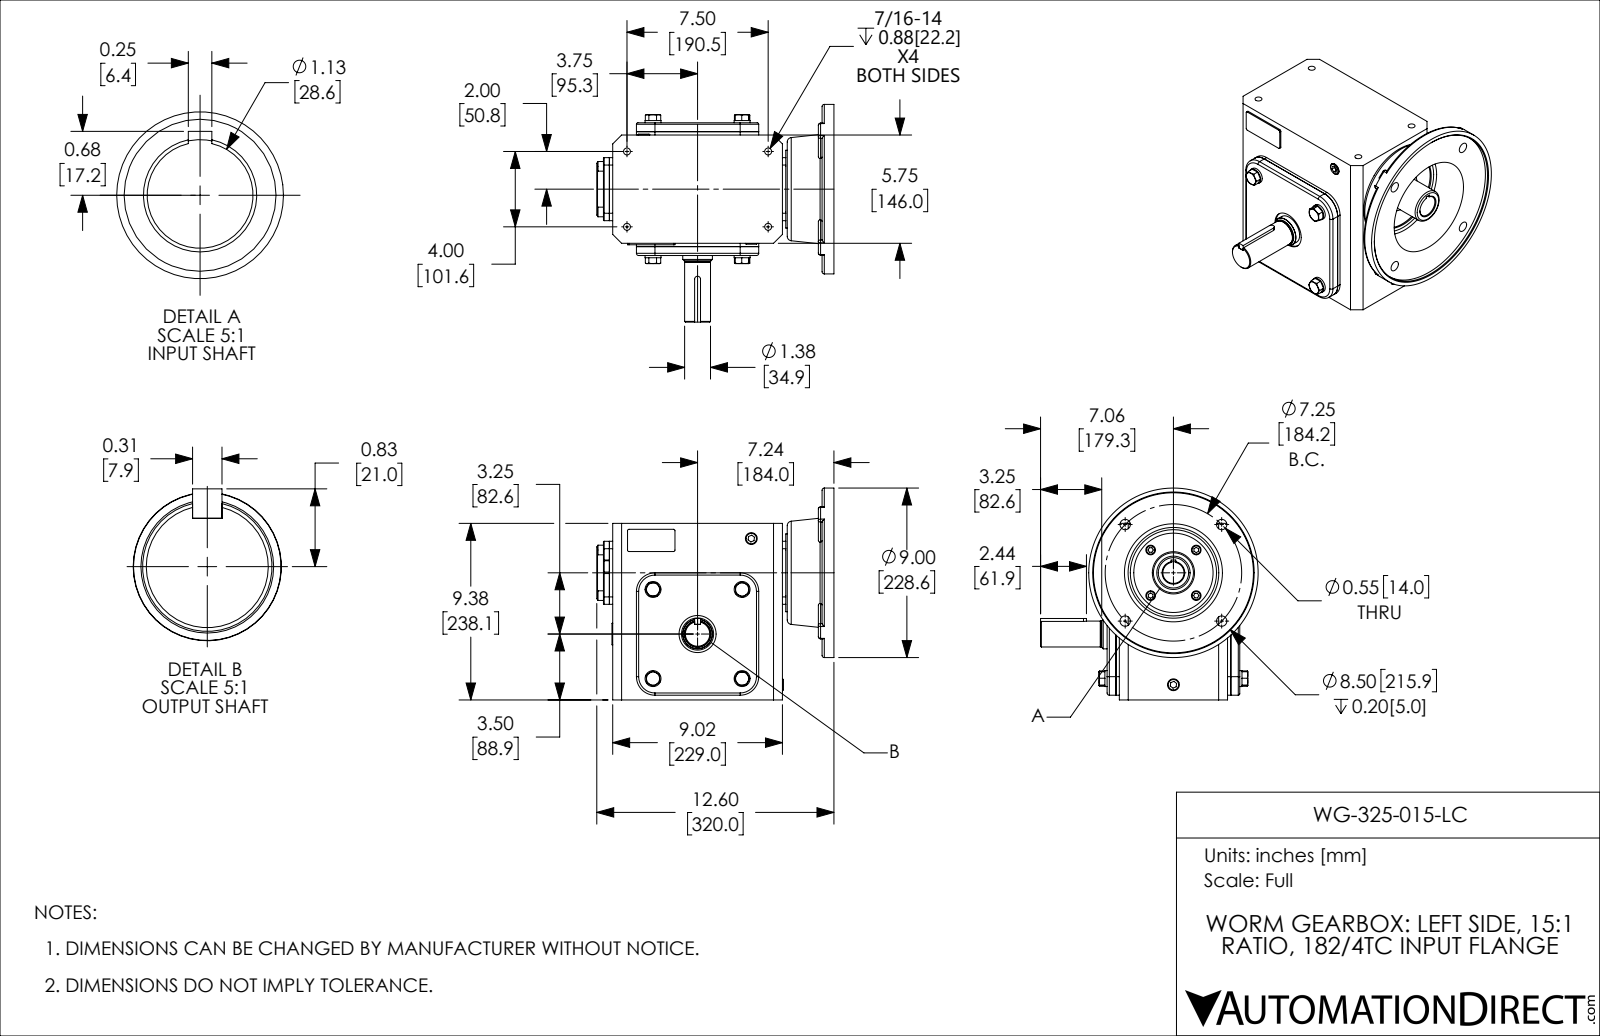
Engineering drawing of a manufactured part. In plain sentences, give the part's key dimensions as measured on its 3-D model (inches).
The part is named "WG-325-015-LC". Its 3-D file was written by "SolidWorks 2017 (AUTOMOTIVE_DESIGN)". It is 40 solids with 653 faces: 336 planar, 195 cylindrical and 122 other. Overall it measures 12.598 by 11.559 by 11.25 inches. Its volume is 529.7 cubic inches and its surface area 1 026 square inches. Round holes: 4 of diameter 0.354, 4 of diameter 0.368, 4 of diameter 0.551, 3 of diameter 0.628, 1 of diameter 0.591, 1 of diameter 0.978, 1 of diameter 1.125, 1 of diameter 1.181, 1 of diameter 1.969, 1 of diameter 2.244, 1 of diameter 2.441, 1 of diameter 2.756. Round bosses or shafts: 4 of diameter 0.846, 4 of diameter 0.512, 1 of diameter 9, 1 of diameter 4.134, 1 of diameter 2.835, 1 of diameter 1.772, 1 of diameter 1.575, 1 of diameter 1.375. Partial cylindrical surfaces (rounded edges, fillets, slot ends): 14 of radius 0.118, 11 of radius 0.079, 4 of radius 0.394, 4 of radius 0.906, 4 of radius 0.984, 2 of radius 0.02, 2 of radius 0.039, 1 of radius 0.156. The main face-to-face distances are 0.079, 0.177, 6.496, 0.394, 6.969, 0.472, 6.575, 6.398, 0.571, 0.65. The hole center spacings are 4.009, 1.713, 1.913, 2.422, 3.625, 5.127, 5.338, 2.372.
